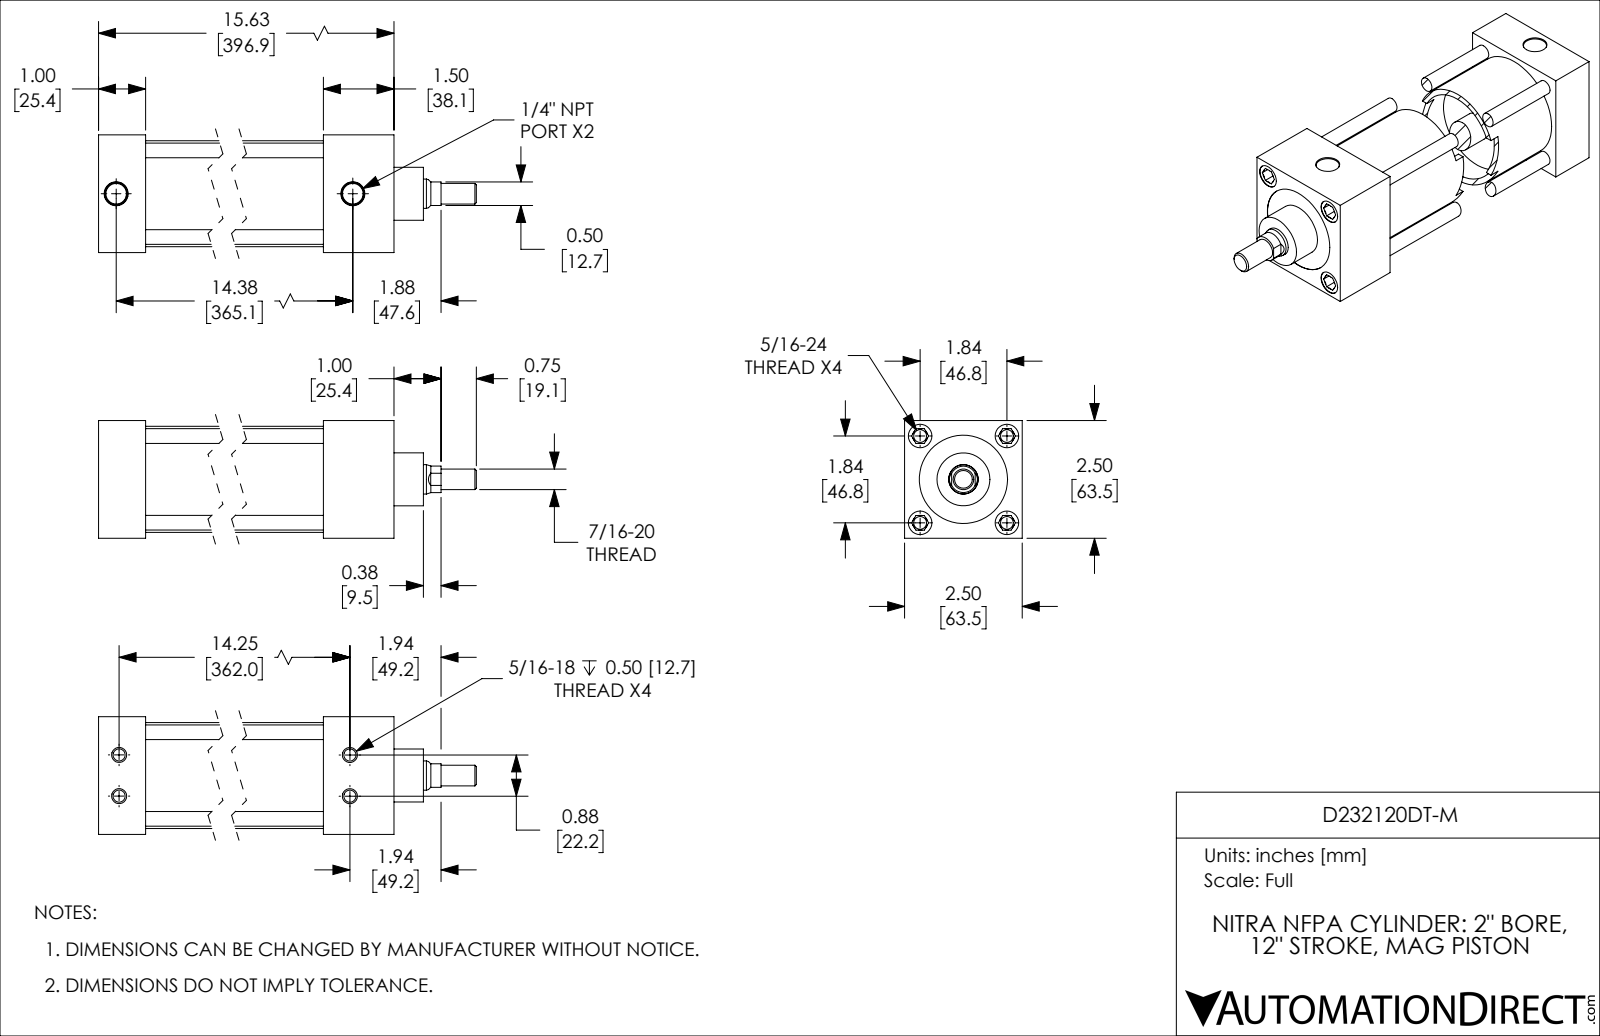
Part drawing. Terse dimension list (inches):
name: D232120DT-M_BODY; D232120DT-M_PISTON_KK1; D232120DT-M
written by: SolidWorks 2019 (CONFIG_CONTROL_DESIGN)
unit: in
bodies: 2 solids, 200 faces (58 planar, 62 cylindrical, 80 other)
size: 17.375 × 2.5 × 2.5
volume: 37.81 in³; area: 332.7 in²
holes: 7× ⌀0.272, 4× ⌀0.257, 4× ⌀0.5, 2× ⌀0.438, 1× ⌀0.626, 1× ⌀1.875, 1× ⌀2.001
bosses: 4× ⌀0.312, 1× ⌀2.251, 1× ⌀1.999, 1× ⌀1.125, 1× ⌀0.624, 1× ⌀0.437
rounds: 1× R0.281
face distances: 2.5, 1, 14.125, 13.125, 1.125, 2.125, 12, 15.625, 14.625, 13.5
hole spacings: 1.84, 1.844, 1.301, 0.441, 0.443, 0.875, 1.304, 2.602
